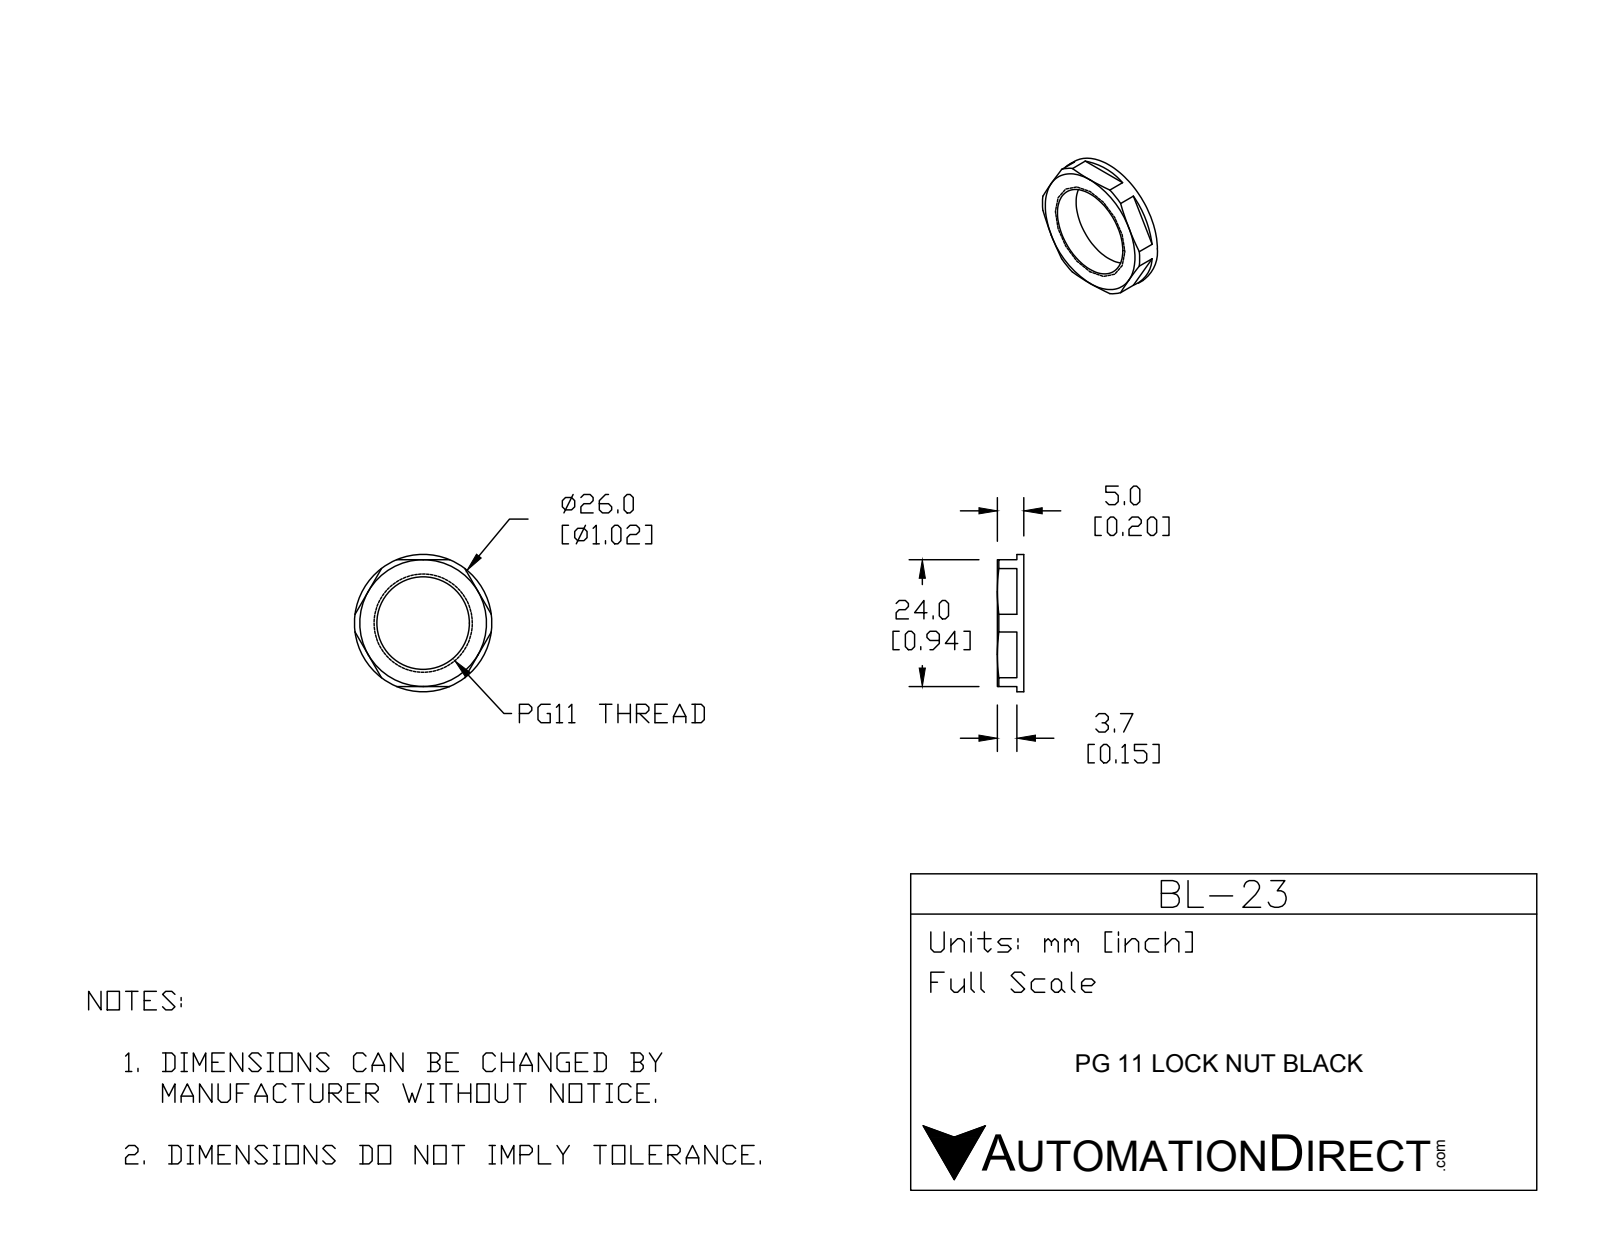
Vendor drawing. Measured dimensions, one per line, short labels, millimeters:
name: BL-23
written by: SolidWorks 2015 (CONFIG_CONTROL_DESIGN)
unit: mm
bodies: 1 solid, 33 faces (17 planar, 10 cylindrical, 6 other)
size: 26 × 26 × 5
volume: 1 297 mm³; area: 1 253 mm²
holes: 3× ⌀1.5, 1× ⌀17.5
bosses: 1× ⌀26
face distances: 5, 24, 1.3, 3.7, 1, 4.7
hole spacings: 11.55, 20, 20.01
